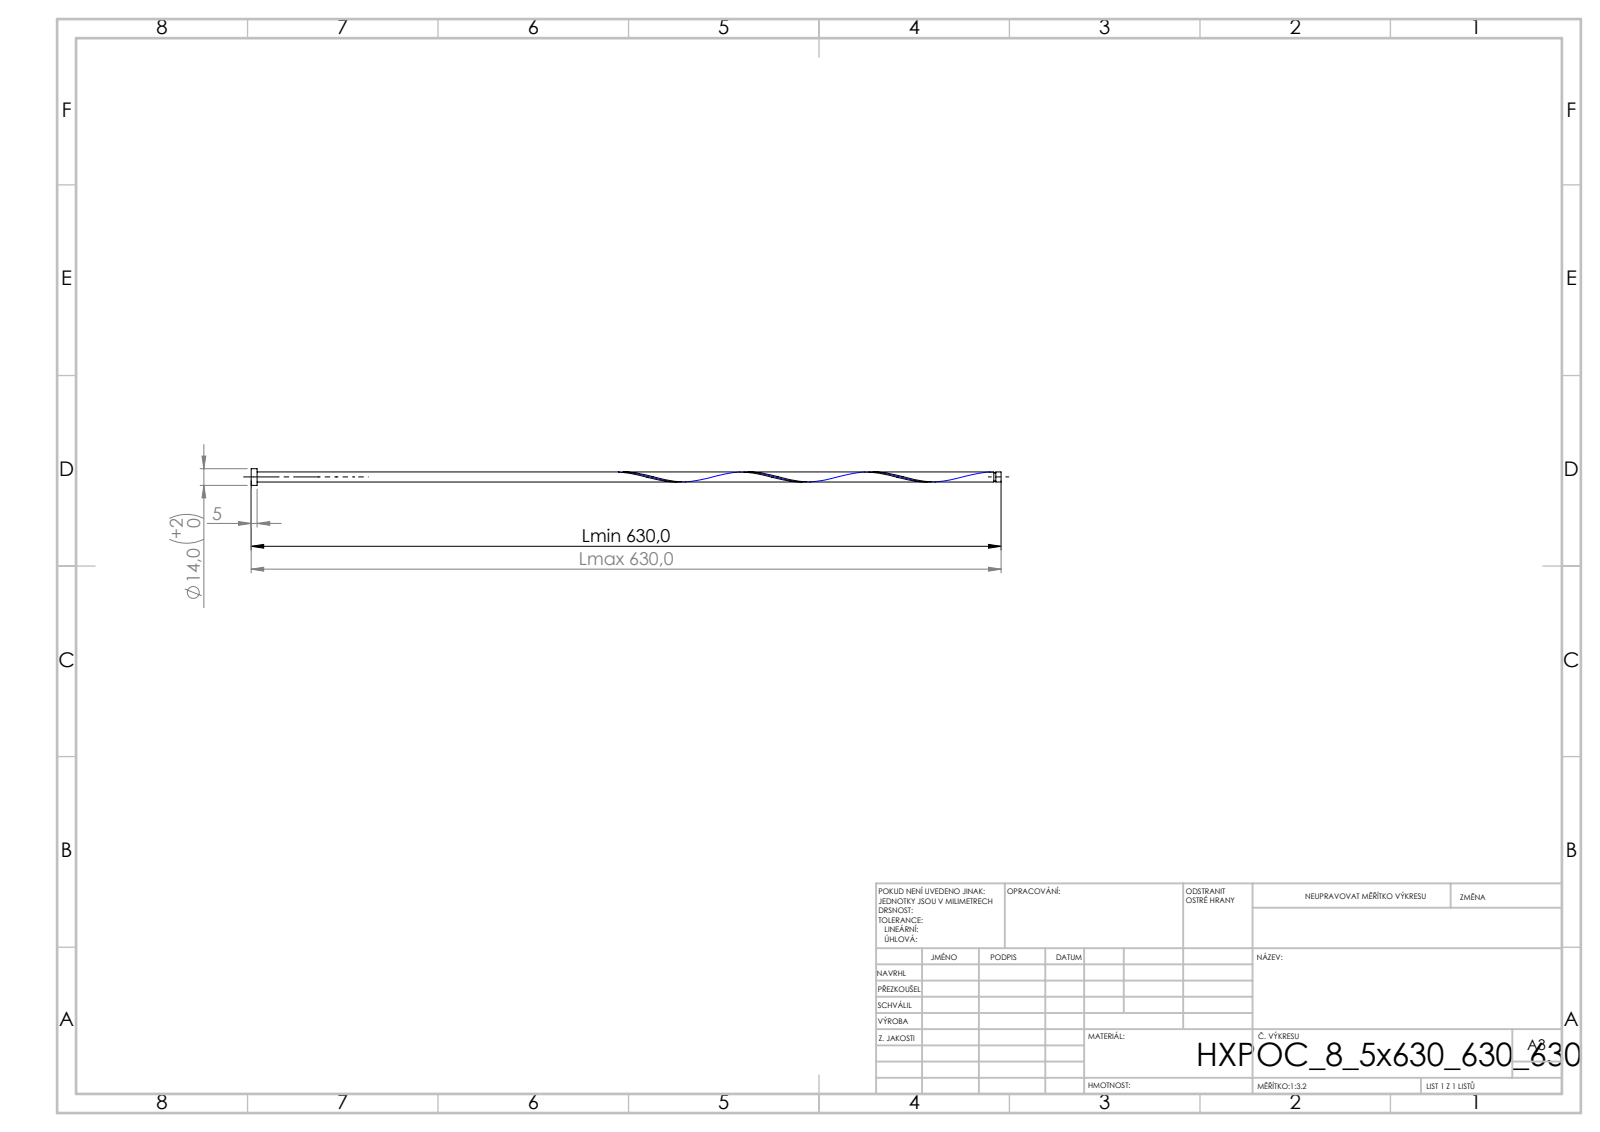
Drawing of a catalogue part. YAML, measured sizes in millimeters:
step_written_by: "SolidWorks 2019 (CONFIG_CONTROL_DESIGN)"
units: millimeters
bodies: {solids: 1, faces: 16, planar: 6, cylindrical: 9, other: 1}
overall_size: [630, 14, 14]
volume: 43802
surface_area: 23119
round_bosses_or_shafts:
  - {diameter: 14, count: 1}
  - {diameter: 8.5, count: 1}
  - {diameter: 6.8, count: 1}
face_to_face_distances: [5, 630, 625, 625.55, 620.55, 4.45, 623.85, 618.85, 1.7, 6.15]
